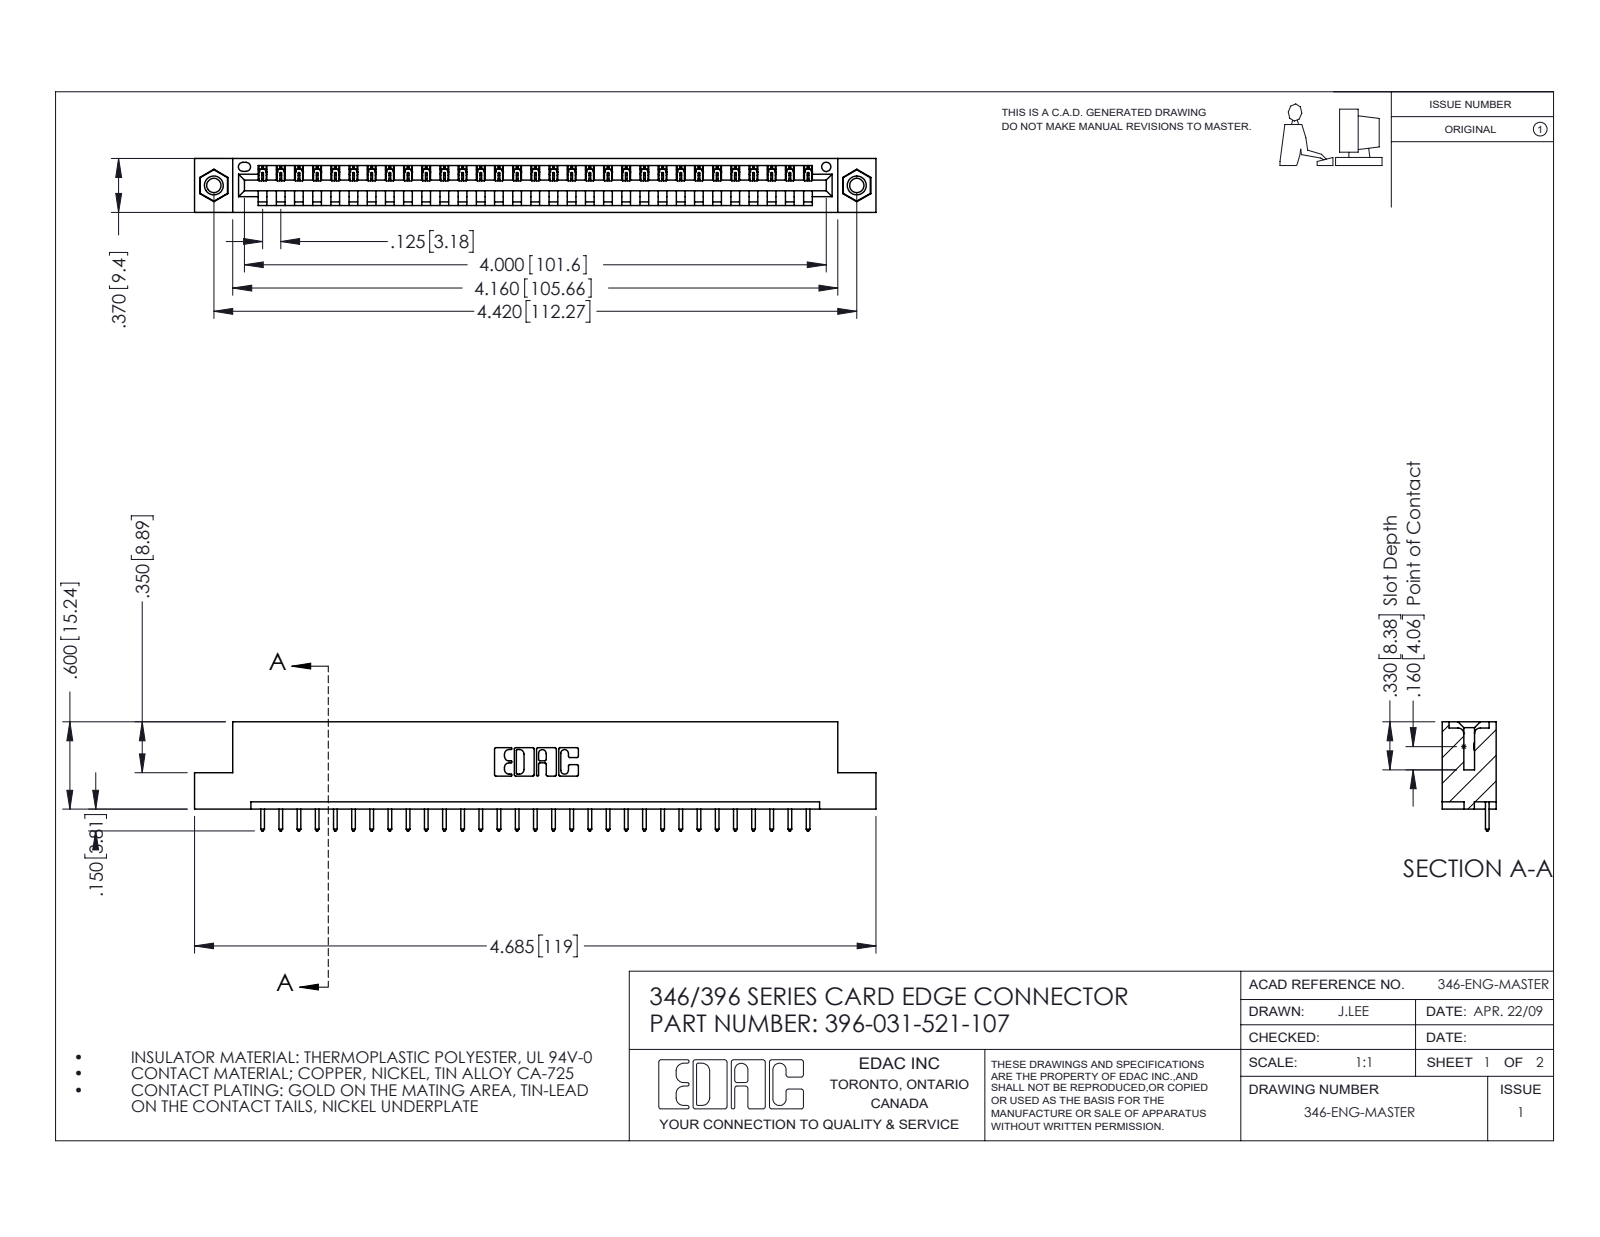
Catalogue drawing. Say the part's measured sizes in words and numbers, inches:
The part is named "345-292-001_345-293-121; 346 Part_Flush Mounting Lugs - 0.156 Dia-TI; 396-031-521-107; 345-250-001_345-250-005-103". Its 3-D file was written by "SolidWorks 2016 (CONFIG_CONTROL_DESIGN)". It is 34 solids with 1980 faces: 1348 planar, 616 cylindrical and 16 other. Overall it measures 4.685 by 0.75 by 0.37 inches. Its volume is 0.684 cubic inches and its surface area 21.05 square inches. Round holes: 2 of diameter 0.098, 2 of diameter 0.125, 2 of diameter 0.156, 1 of diameter 0.064. Round bosses or shafts: 2 of diameter 0.155. Partial cylindrical surfaces (rounded edges, fillets, slot ends): 62 of radius 0.006, 62 of radius 0.01, 22 of radius 0.01, 6 of radius 0.007, 6 of radius 0.031, 3 of radius 0.026, 2 of radius 0.031, 2 of radius 0.04. The main face-to-face distances are 0.048, 0.322, 0.37, 0.25, 0.072, 0.298, 0.025, 0.148, 0.222, 0.1. The hole center spacings are 0.246, 4.212, 4.42.
